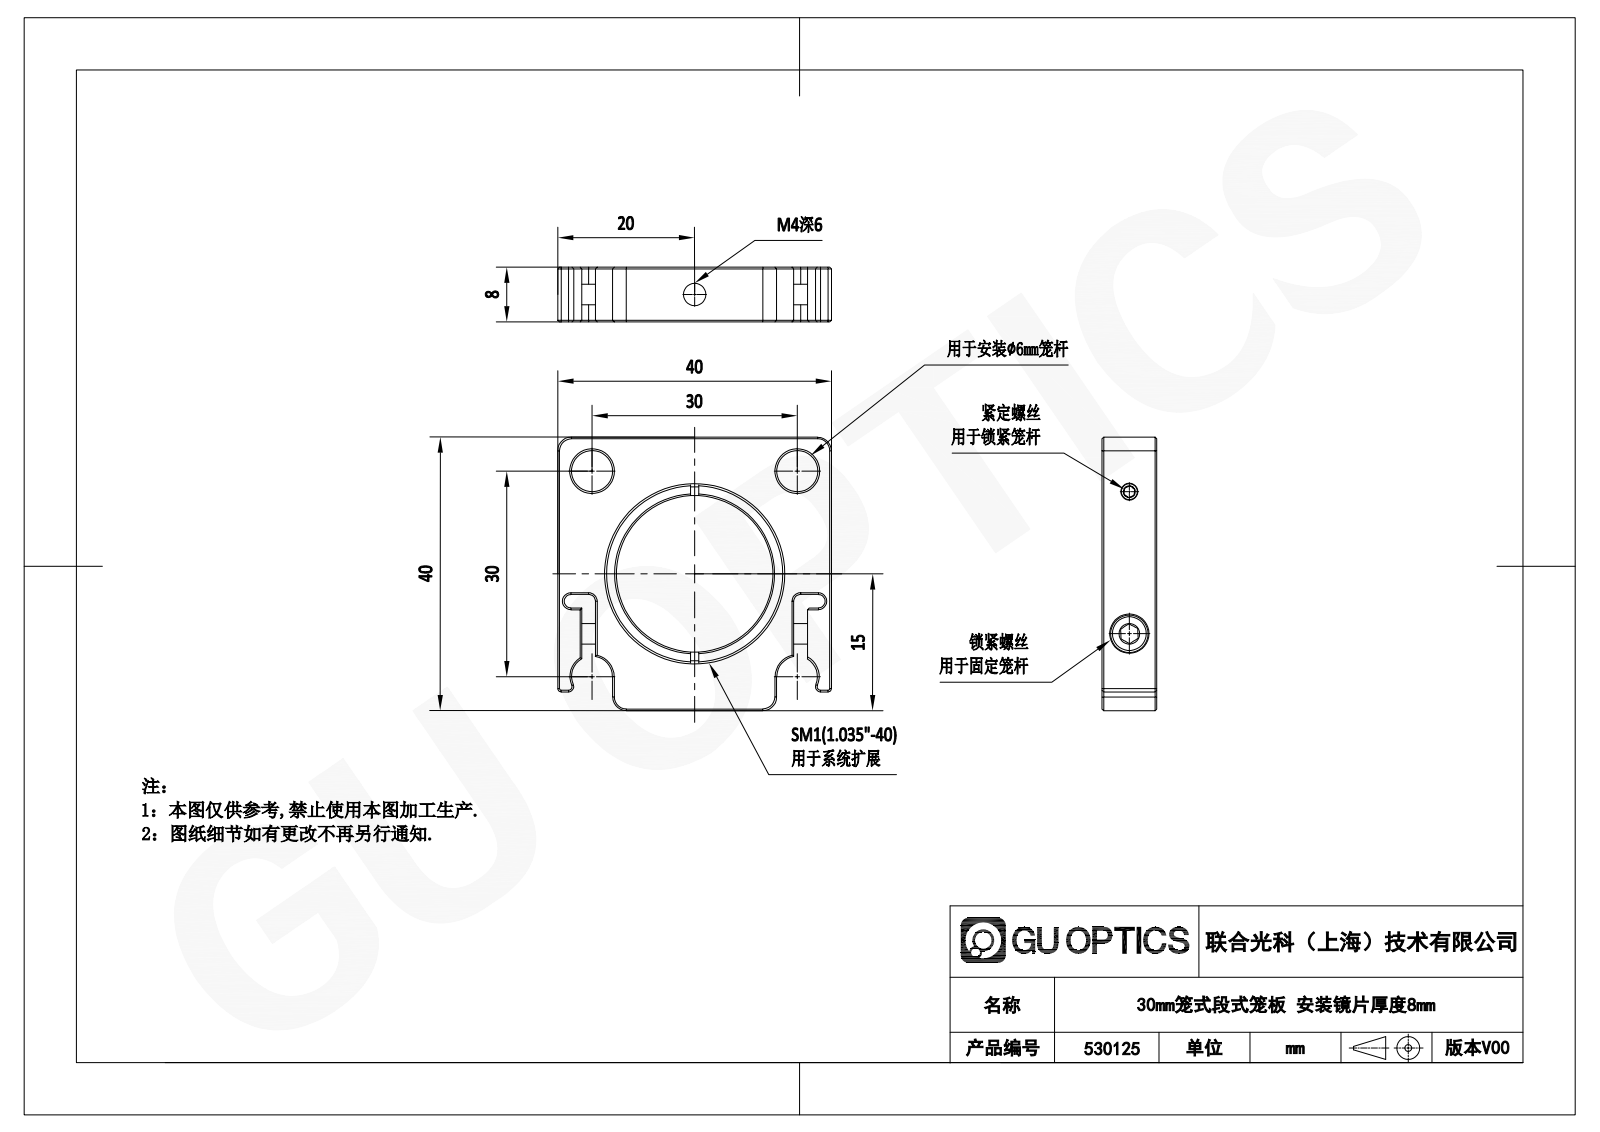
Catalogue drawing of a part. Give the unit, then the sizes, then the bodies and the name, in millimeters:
Units: millimetres
Overall size (bounding box): 40 × 40 × 8
Round holes (diameter × count): ⌀2.5 ×2, ⌀6 ×2, ⌀3.3 ×1, ⌀3.4 ×1, ⌀5.8 ×1, ⌀22.9 ×1, ⌀25.4 ×1
Round bosses / shafts (diameter × count): ⌀3 ×2, ⌀26.29 ×1, ⌀5.5 ×1
Partial cylindrical surfaces — rounded edges, fillets, slot ends (radius × count): R1 ×4, R2 ×4, R0.5 ×2, R0.75 ×2, R3 ×2
Main face-to-face distances: 8, 40, 2, 6, 5.5, 34.5, 3.5, 2.9, 33.9, 36.5
Hole centre spacings: 21.21, 20.75, 30
Volume: 7 442 mm³ · Surface area: 6 004 mm²
Bodies: 7 solids, 224 faces (109 planar, 38 cylindrical, 77 other)
Part name (STEP PRODUCT): 530125
STEP written by: SolidWorks 2020 (CONFIG_CONTROL_DESIGN)
